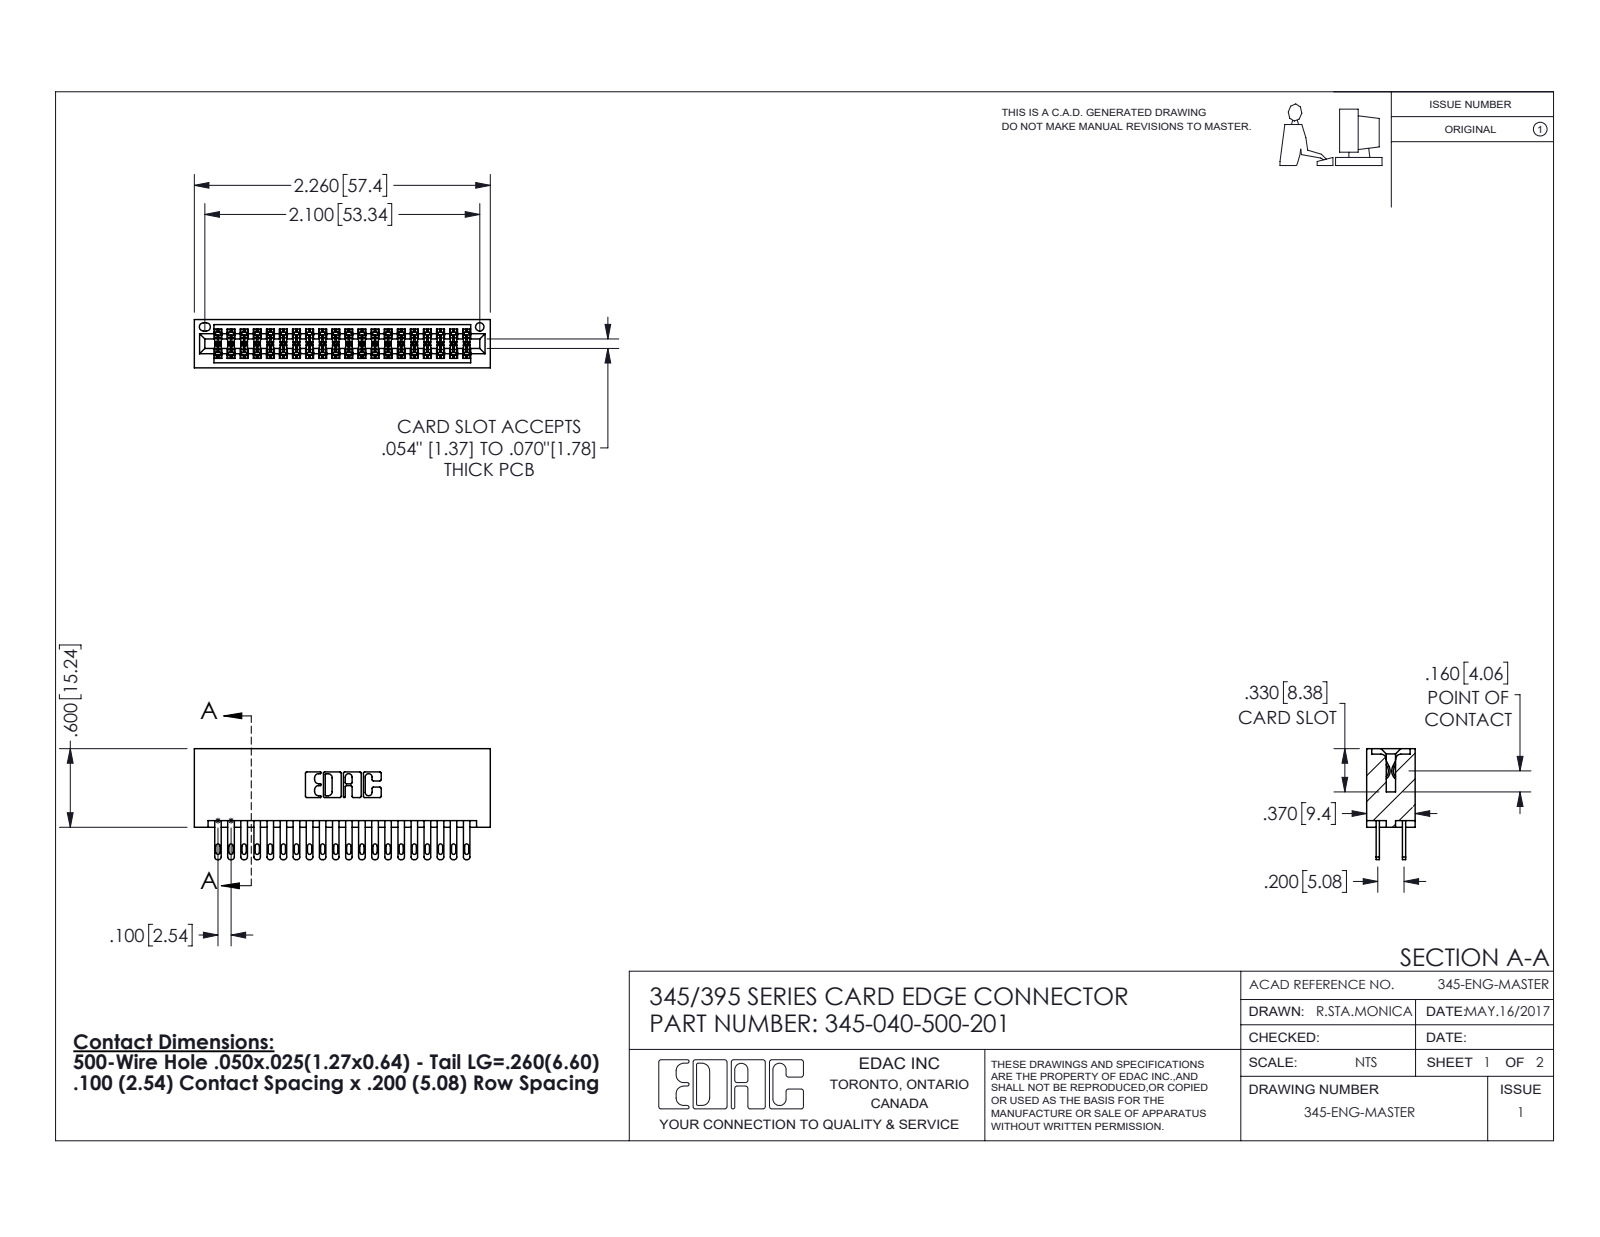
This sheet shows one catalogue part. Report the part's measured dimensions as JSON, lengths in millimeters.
{"part_name": "345-040-500-201; 345 Part_No Mounting Lugs; 345-292-001_345-293-100", "step_written_by": "SolidWorks 2016 (CONFIG_CONTROL_DESIGN)", "units": "millimeters", "bodies": {"solids": 41, "faces": 1958, "planar": 1156, "cylindrical": 802, "other": 0}, "overall_size": [57.4, 21.5, 9.4], "volume_mm3": 6110, "surface_area_mm2": 9316, "round_holes": [[1.6, 1]], "partial_cylinders_radius": [[0.2, 60], [0.4, 40], [0.5, 40], [0.3, 22], [0.2, 6], [0.8, 6], [0.7, 3], [0.4, 2]], "face_to_face_distances": [7.6, 1.8, 5.1, 2.5, 6.9, 0.6, 9.4, 5.7, 4.4, 2.5]}
